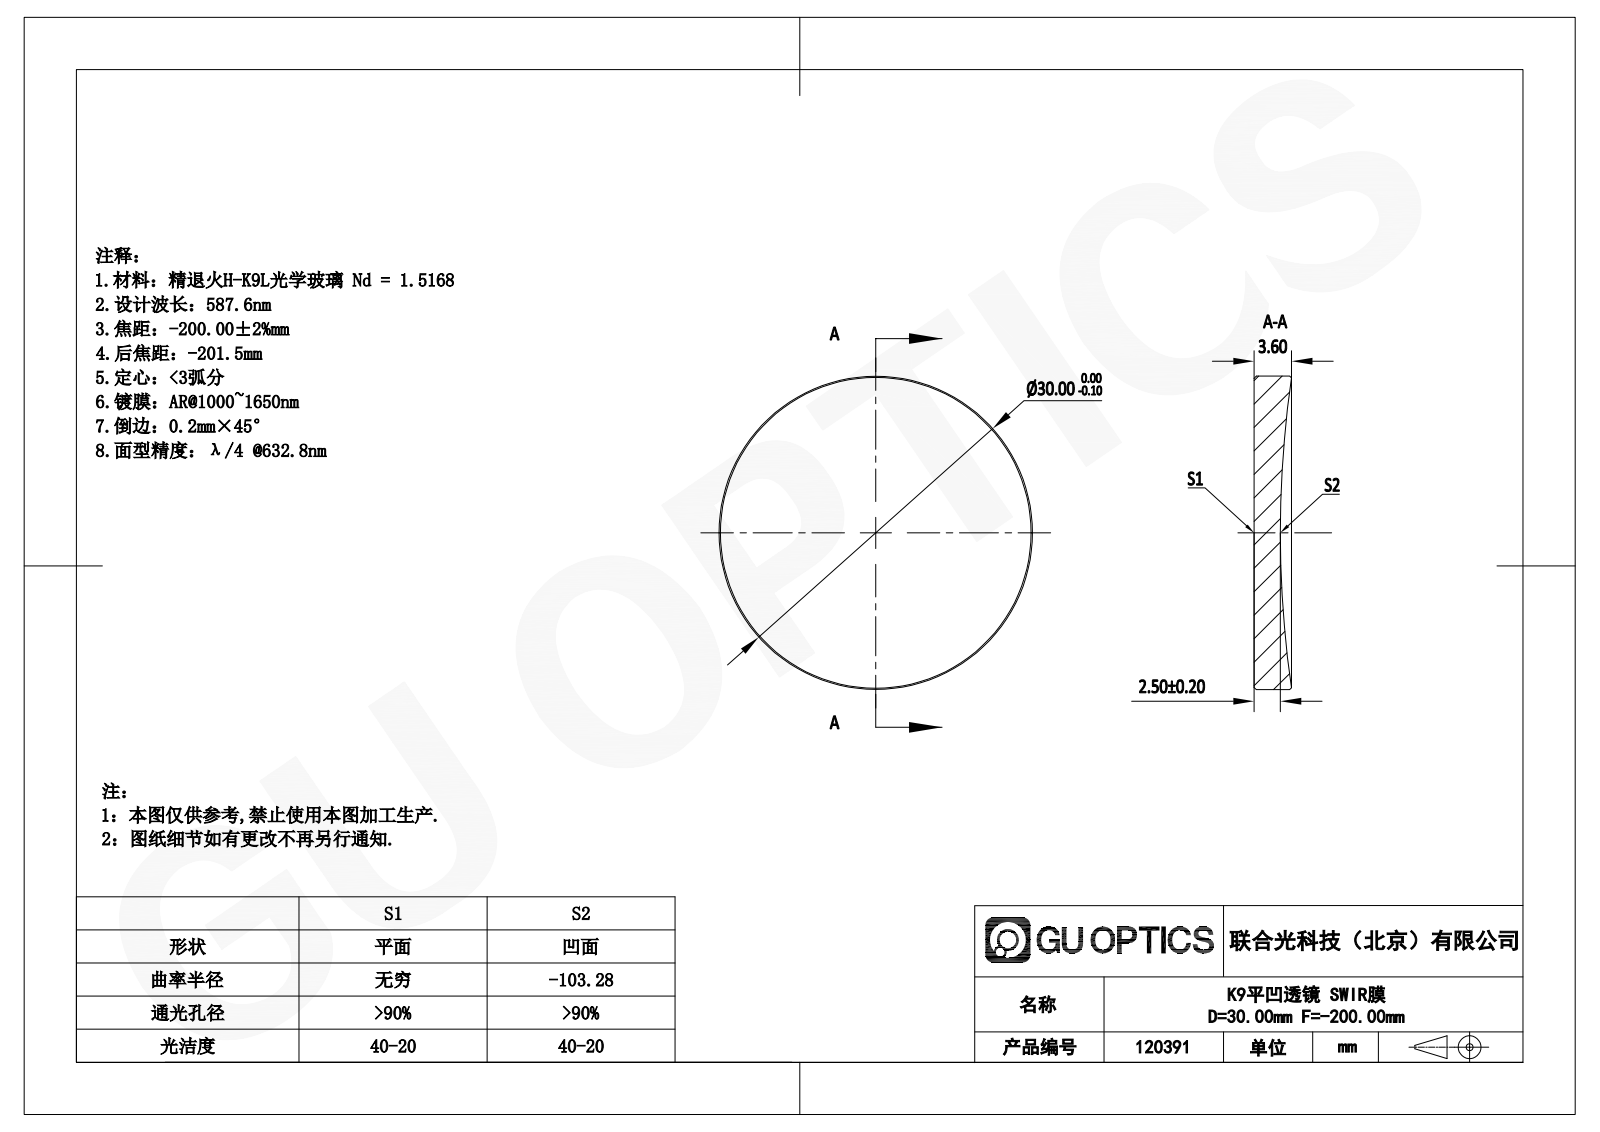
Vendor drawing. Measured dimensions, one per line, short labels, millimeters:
name: GL13-030-200
written by: SolidWorks 2022 (AUTOMOTIVE_DESIGN)
unit: mm
bodies: 1 solid, 9 faces (1 planar, 2 cylindrical, 6 other)
size: 30 × 30 × 3.57
volume: 2 152 mm³; area: 1 733 mm²
bosses: 1× ⌀30
